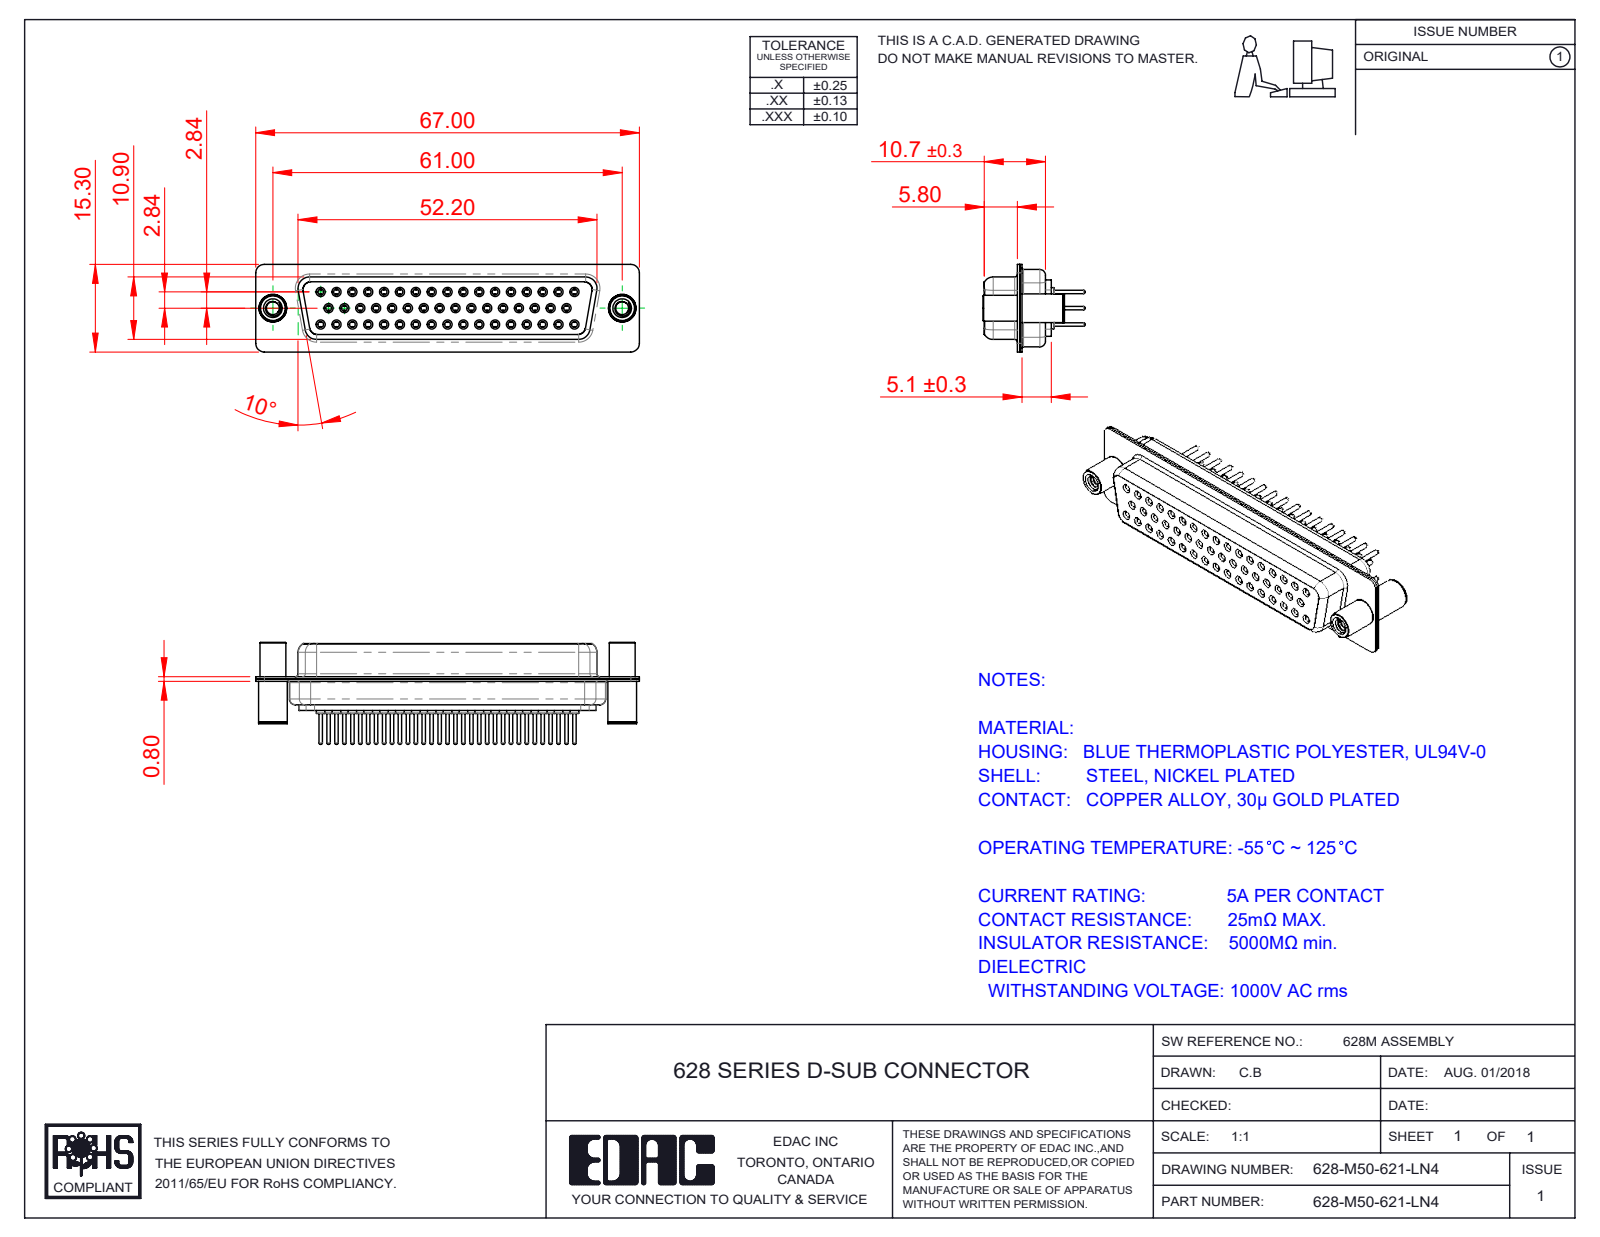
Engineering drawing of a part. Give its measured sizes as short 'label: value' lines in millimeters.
name: 628M Housing_50 Contacts; 628M Contact Row 1_21; 628M Shell Rear_50 Contacts; 628M Contact Row 3_21 (+4 more)
written by: SolidWorks 2020 (CONFIG_CONTROL_DESIGN)
unit: mm
bodies: 55 solids, 3115 faces (823 planar, 1139 cylindrical, 1153 other)
size: 67 × 17.8 × 15.3
volume: 6 909 mm³; area: 15 567 mm²
holes: 50× ⌀1, 50× ⌀1.1, 50× ⌀1.7, 50× ⌀1.8, 50× ⌀2, 2× ⌀2.26, 2× ⌀3.26, 2× ⌀4, 2× ⌀4.8
bosses: 50× ⌀2.2, 50× ⌀1.6, 50× ⌀1.5, 50× ⌀0.6, 2× ⌀5, 2× ⌀4.9, 2× ⌀4.5
rounds: 16× R1.5, 12× R2, 8× R1.35, 8× R1.6, 4× R0.25, 4× R0.5, 4× R0.6, 4× R0.65
face distances: 0.4, 1.3, 11.8, 0.9, 5.5, 5.9, 0.85, 13.1, 5.8, 10.5
hole spacings: 3.16, 2.77, 5.54, 8.31, 11.08, 13.85, 16.62, 19.39
